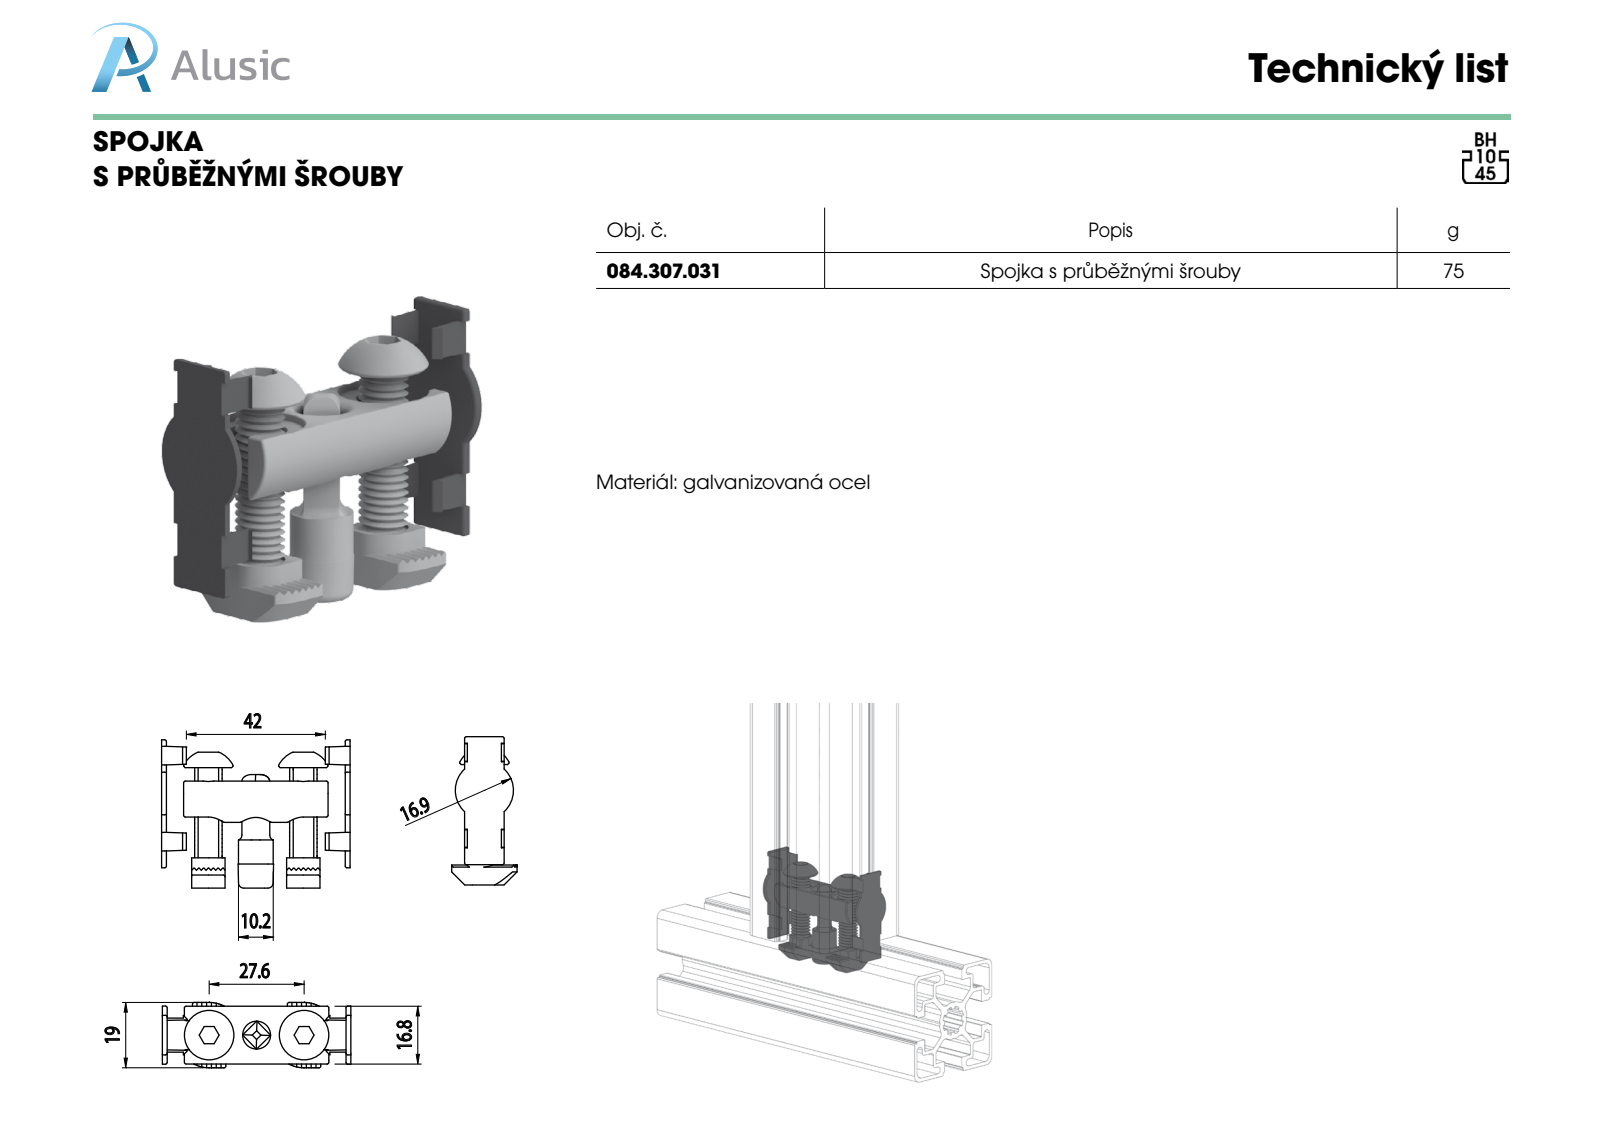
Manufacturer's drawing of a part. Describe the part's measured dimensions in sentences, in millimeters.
The part is named "084.307.031". Its 3-D file was written by "SolidWorks 2011 (CONFIG_CONTROL_DESIGN)". It is 8 solids with 563 faces: 222 planar, 231 cylindrical and 110 other. Overall it measures 54.8 by 43.1 by 19 millimeters. Its volume is 12 793 cubic millimeters and its surface area 11 550 square millimeters. Round holes: 2 of diameter 6.6, 1 of diameter 8.1. Round bosses or shafts: 2 of diameter 8, 1 of diameter 10.1. Partial cylindrical surfaces (rounded edges, fillets, slot ends): 40 of radius 0.5, 14 of radius 0.2, 6 of radius 0.3, 4 of radius 0.1, 4 of radius 1.5, 4 of radius 2, 4 of radius 5, 2 of radius 4.2. The main face-to-face distances are 1.4, 53.4, 54.8, 52, 5, 0.75, 9.15, 7.35, 35, 9.7. The hole center spacings are 13.8, 27.6.
